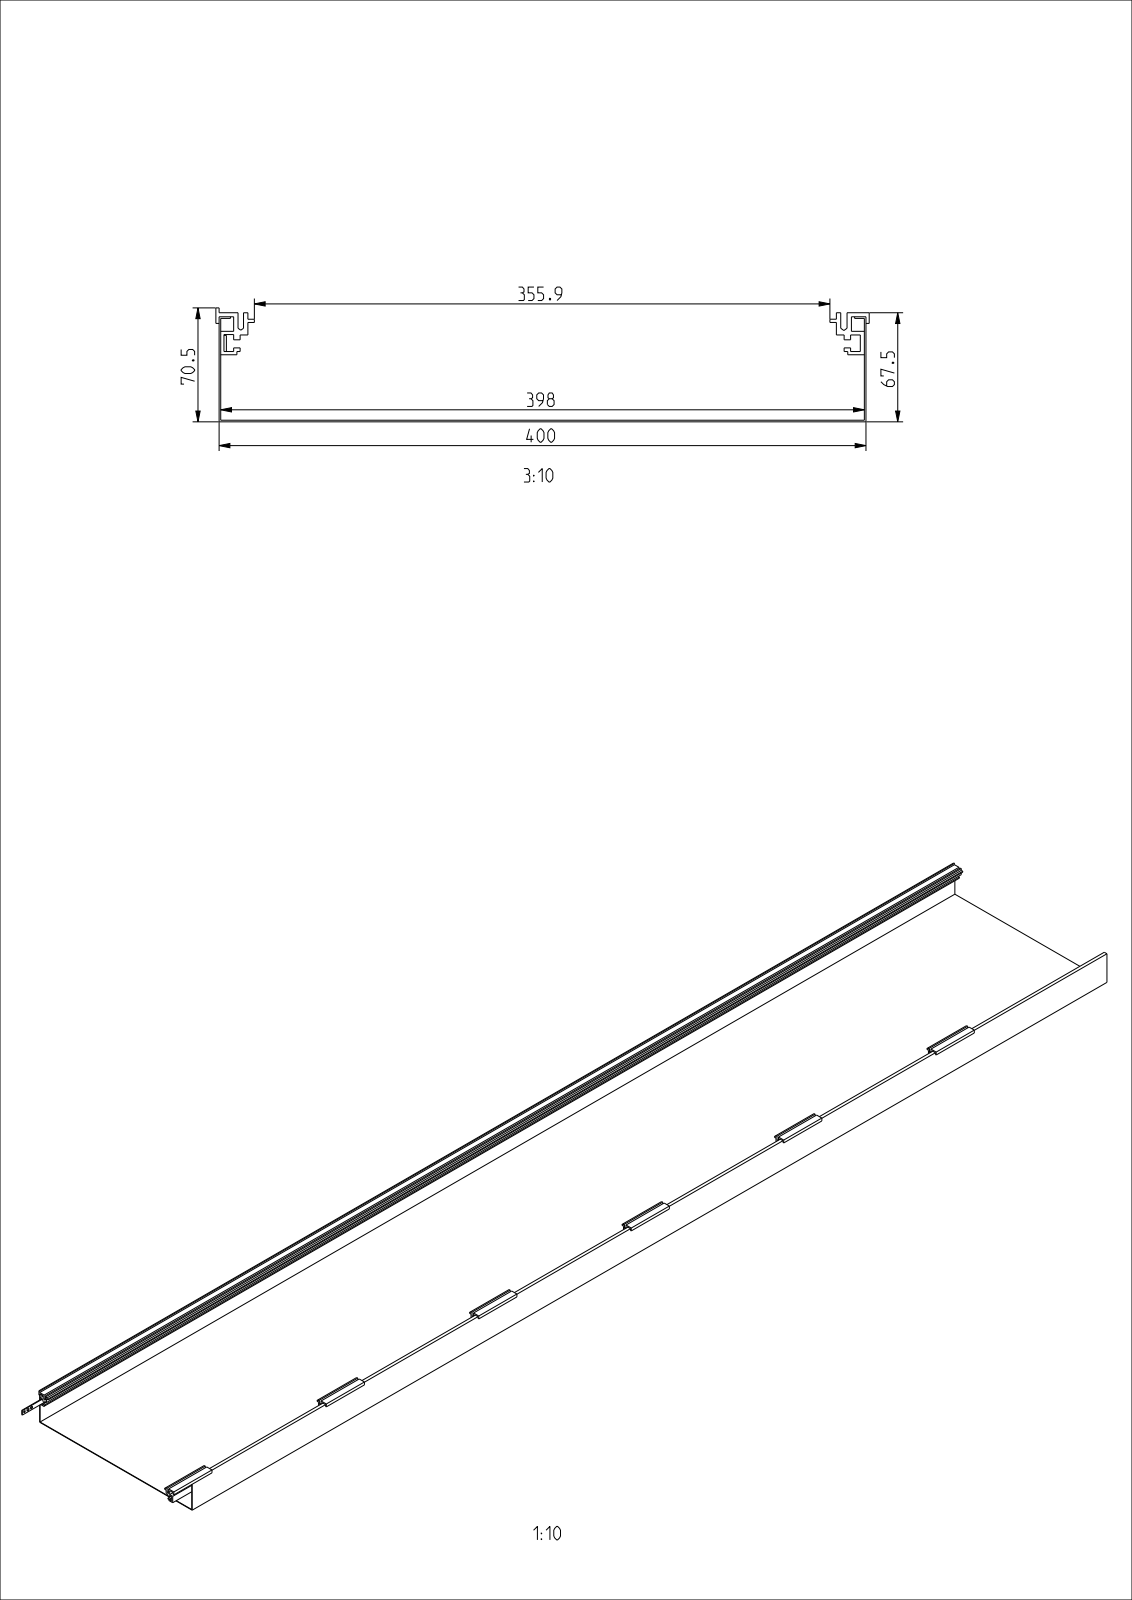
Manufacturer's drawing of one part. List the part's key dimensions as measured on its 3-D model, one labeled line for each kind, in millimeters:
Part name (STEP PRODUCT): AKU4000701_WANNE_3; AKU_SEITENPROFIL_APA_K24_6; ZES_VK180_KUN_3; AKU_SEITENPROFIL_APA_O01_4 (+2 more)
STEP written by: CREO PARAMETRIC BY PTC INC, 2022281 (AUTOMOTIVE_DESIGN)
Units: millimetres
Bodies: 9 solids, 265 faces (253 planar, 12 cylindrical, 0 other)
Overall size (bounding box): 2450 × 404 × 70.5
Volume: 1 941 000 mm³ · Surface area: 3 142 000 mm²
Round holes (diameter × count): ⌀5.5 ×4, ⌀4.2 ×2
Main face-to-face distances: 1, 399, 400, 398, 2, 64, 8, 3, 9, 65
Hole centre spacings: 9.25, 66.5, 18.5, 57.25, 75.75, 48, 85
